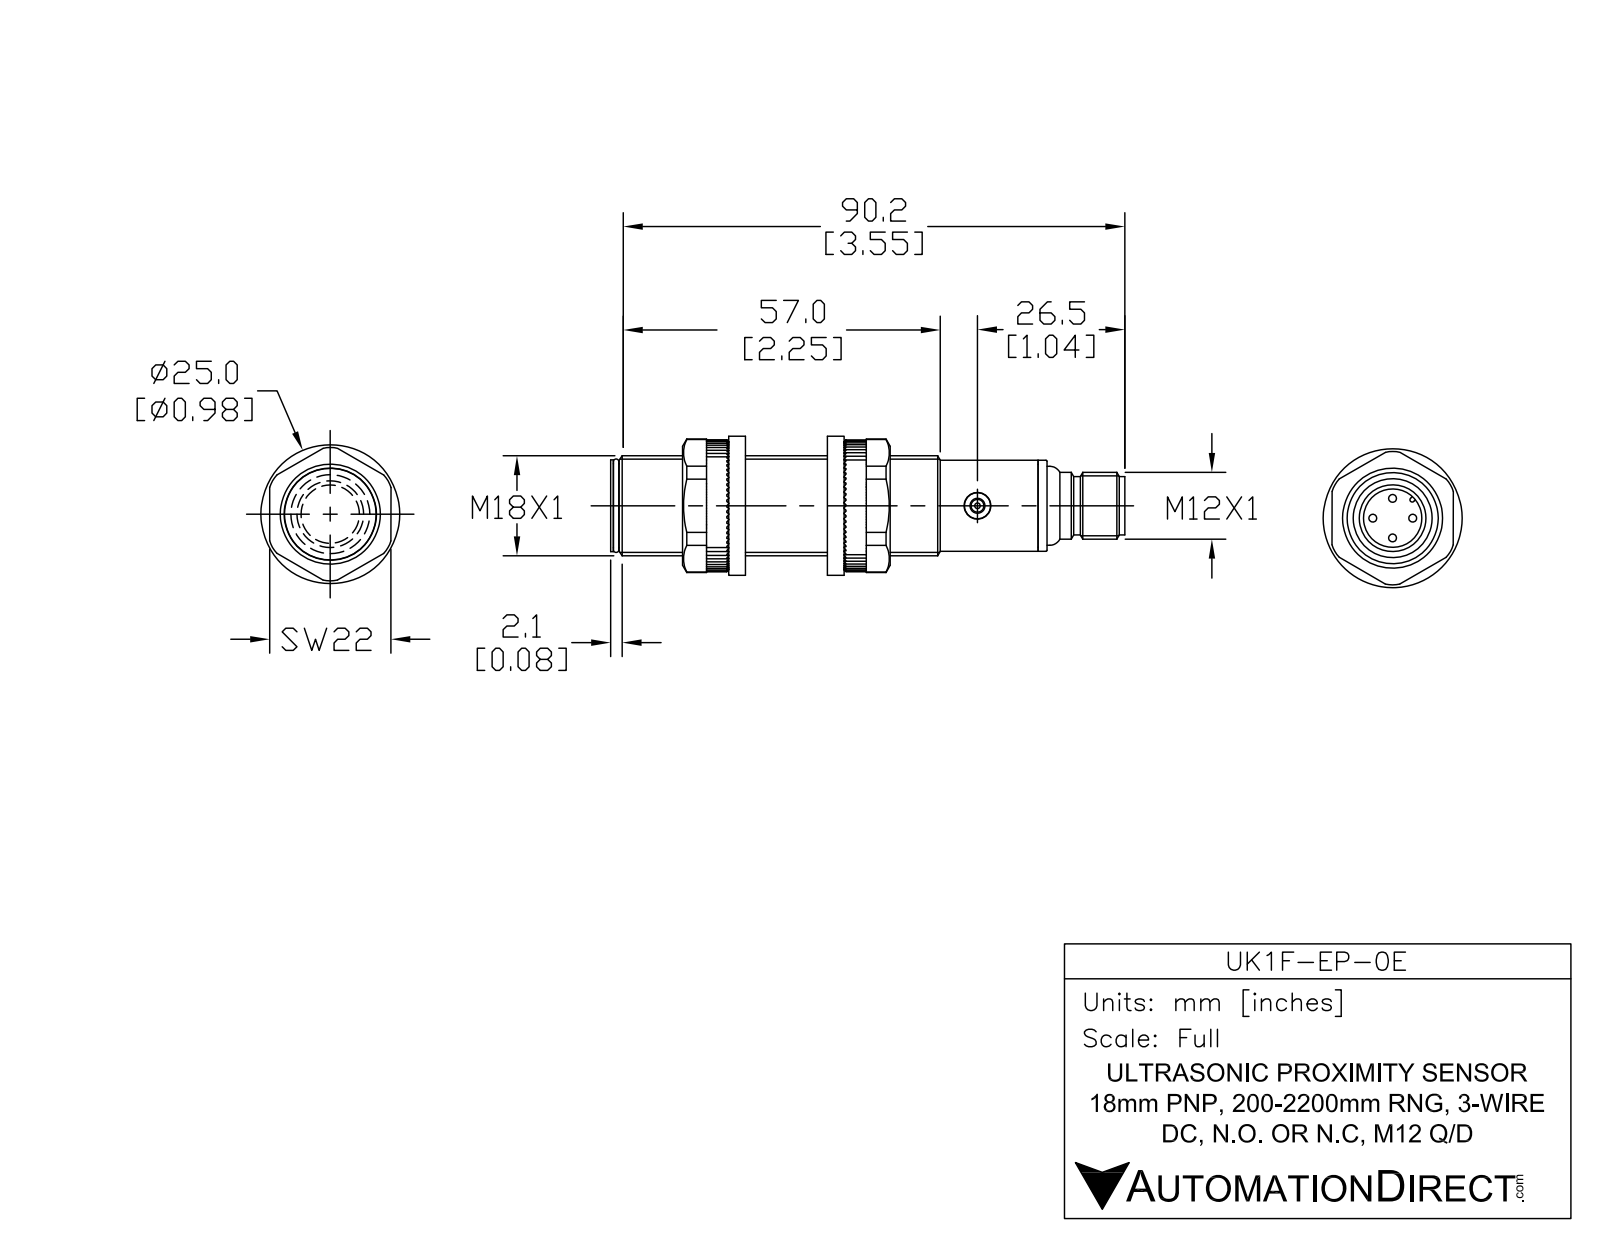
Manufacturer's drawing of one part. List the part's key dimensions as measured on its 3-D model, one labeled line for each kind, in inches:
Part name (STEP PRODUCT): UK1F-EP-0E
STEP written by: SolidWorks 2017 (AUTOMOTIVE_DESIGN)
Units: inches
Bodies: 6 solids, 106 faces (21 planar, 48 cylindrical, 37 other)
Overall size (bounding box): 3.606 × 0.709 × 0.709
Volume: 1.202 in³ · Surface area: 10.68 in²
Round holes (diameter × count): ⌀0.106 ×1, ⌀0.185 ×1, ⌀0.276 ×1, ⌀0.327 ×1, ⌀0.374 ×1
Round bosses / shafts (diameter × count): ⌀0.039 ×4, ⌀0.709 ×1, ⌀0.654 ×1, ⌀0.646 ×1, ⌀0.622 ×1, ⌀0.559 ×1, ⌀0.472 ×1, ⌀0.413 ×1
Partial cylindrical surfaces — rounded edges, fillets, slot ends (radius × count): R0.024 ×1
Main face-to-face distances: 2.957, 0.039, 2.996, 0.037, 2.994, 0.043, 0.157, 3.055, 3.053, 3.016
